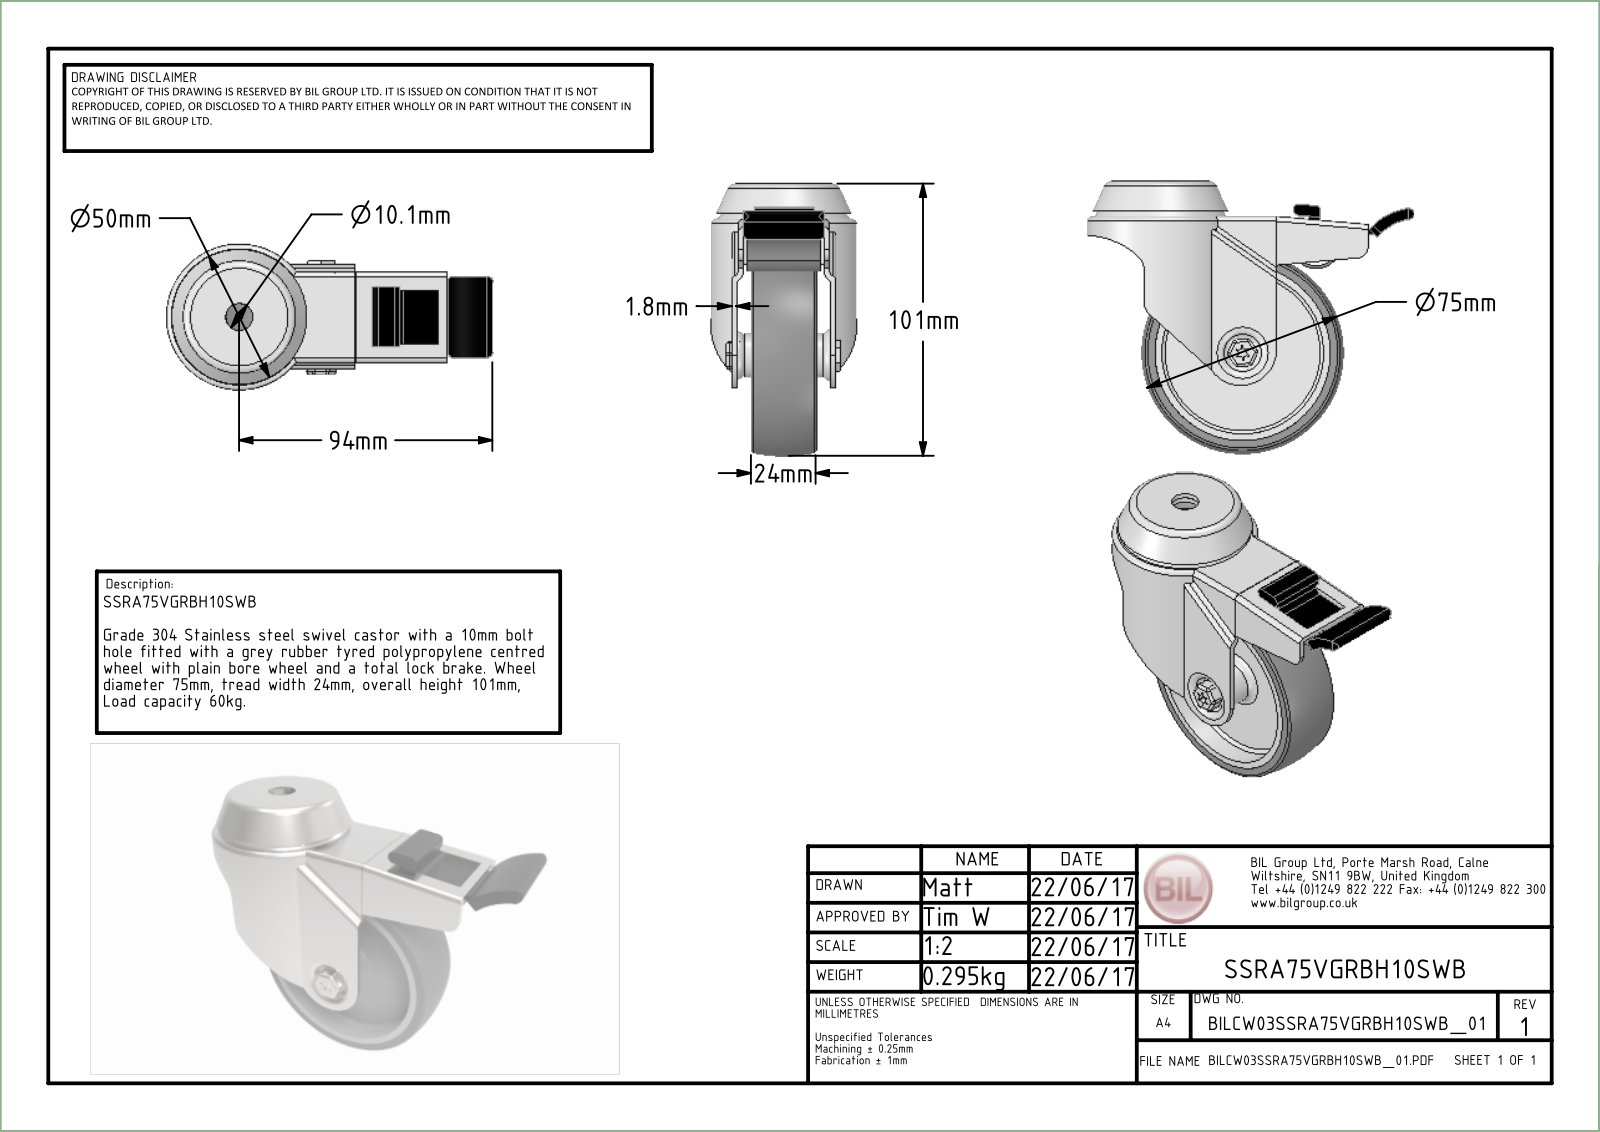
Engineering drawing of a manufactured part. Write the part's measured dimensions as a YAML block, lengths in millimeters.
part_name: "SSRA75VGRBH10SWB v3; SSRA75ASBH10SWB v1; STAINLESS STEEL HEAD; NYLON BRAKE PEDAL (+8 more)"
step_written_by: "Autodesk Translation Framework v13.20.0.188 (AUTOMOTIVE_DESIGN)"
units: millimeters
bodies: {solids: 10, faces: 497, planar: 209, cylindrical: 160, other: 128}
overall_size: [119, 101, 50]
volume: 102623
surface_area: 68958
round_holes:
  - {diameter: 6, count: 1}
  - {diameter: 6.5, count: 1}
  - {diameter: 8.4, count: 1}
  - {diameter: 8.5, count: 1}
  - {diameter: 10.5, count: 1}
  - {diameter: 10.56, count: 1}
  - {diameter: 54, count: 1}
  - {diameter: 60, count: 1}
round_bosses_or_shafts:
  - {diameter: 39, count: 1}
  - {diameter: 18, count: 1}
  - {diameter: 16, count: 1}
  - {diameter: 14.76, count: 1}
  - {diameter: 8, count: 1}
  - {diameter: 7.9, count: 1}
  - {diameter: 5.88, count: 1}
  - {diameter: 4.74, count: 1}
partial_cylinders:
  - {radius: 1, count: 22}
  - {radius: 1.8, count: 22}
  - {radius: 0.5, count: 12}
  - {radius: 1.5, count: 11}
  - {radius: 0.9, count: 10}
  - {radius: 0.4, count: 6}
  - {radius: 2, count: 5}
  - {radius: 3.5, count: 2}
face_to_face_distances: [1.8, 33.8, 3, 2.5, 26.5, 10, 12.5, 16.5, 14, 4.8]
